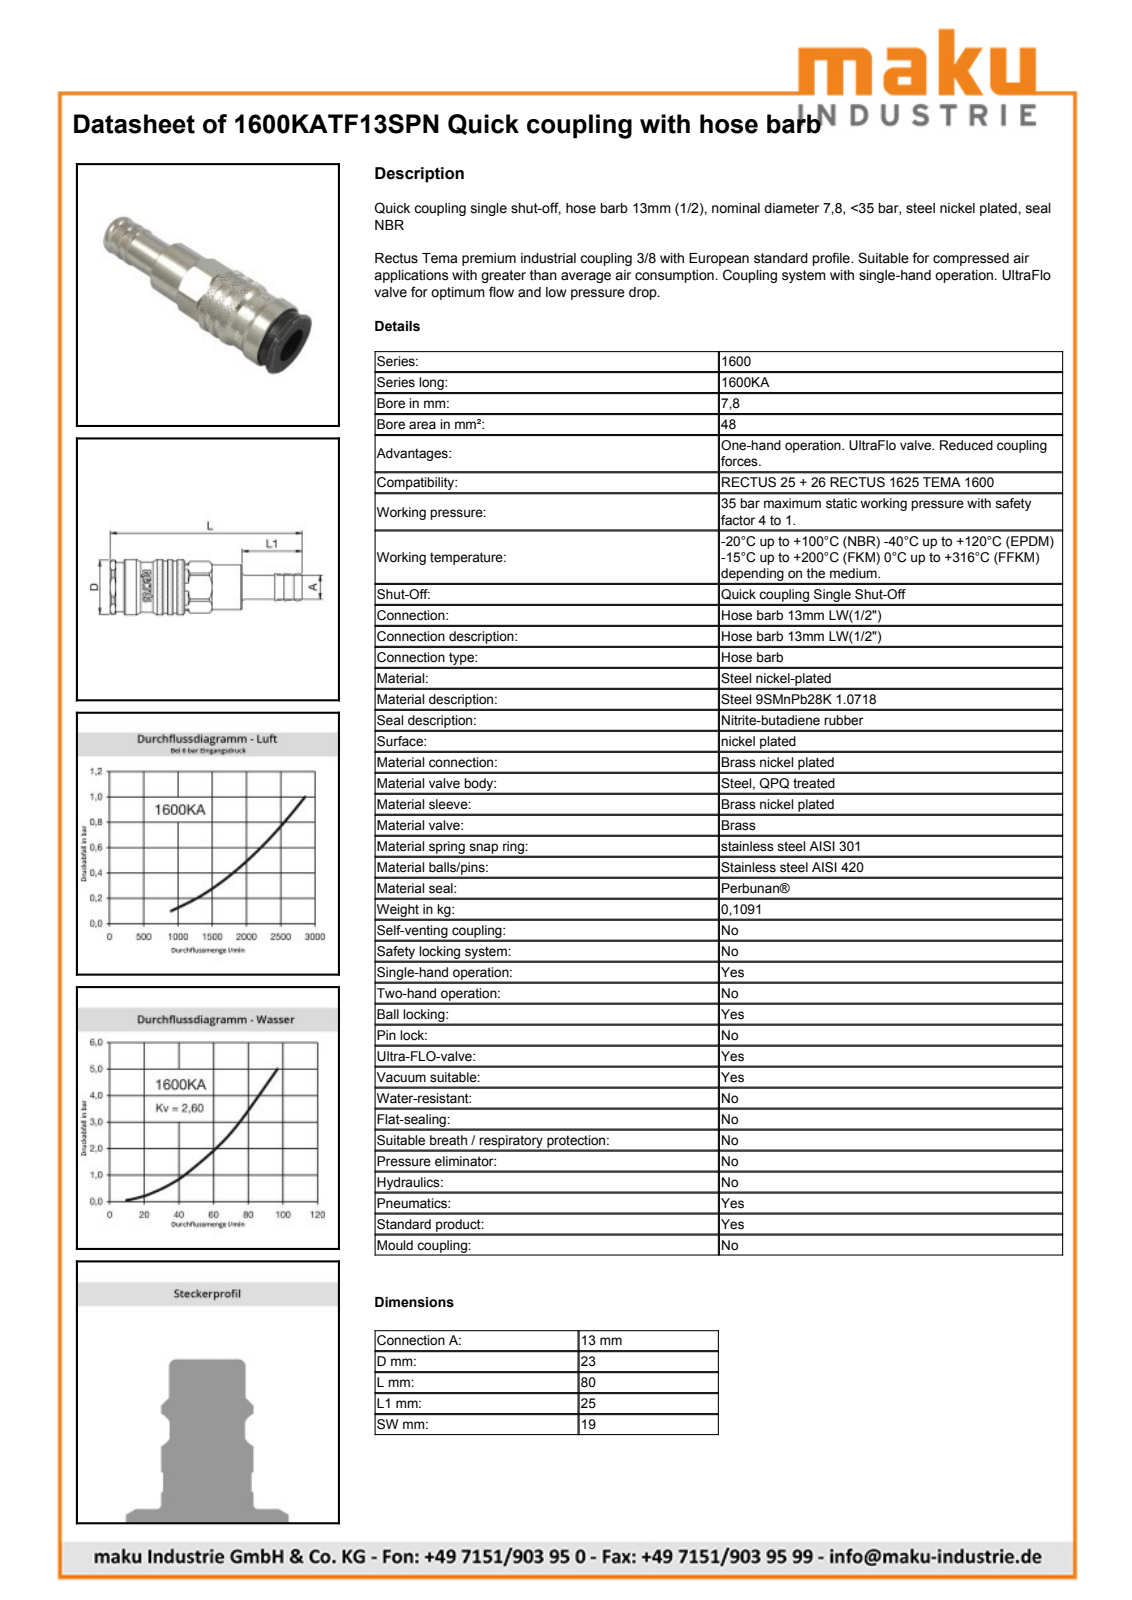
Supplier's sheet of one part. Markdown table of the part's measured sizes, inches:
| quantity | value |
| --- | --- |
| part name | D106873 |
| STEP written by | Autodesk Inventor 2013 (AUTOMOTIVE_DESIGN) |
| units | inches |
| bodies | 2 solids, 637 faces (211 planar, 92 cylindrical, 334 other) |
| overall size | 3.133 × 0.911 × 0.911 |
| volume | 1.283 in³ |
| surface area | 14.91 in² |
| round holes (diameter × count) | 0.636 × 1, 0.677 × 1, 0.705 × 1, 0.772 × 1, 0.815 × 1 |
| round bosses / shafts (diameter × count) | 0.911 × 1, 0.866 × 1, 0.827 × 1, 0.799 × 1, 0.74 × 1, 0.693 × 1, 0.669 × 1, 0.618 × 1 |
| partial cylindrical surfaces (radius × count) | 0.306 × 1, 0.38 × 1, 0.409 × 1, 0.421 × 1, 0.443 × 1 |
| main face-to-face distances | 0.748, 3.133, 2.149, 0.984, 1.222, 0.927, 1.911, 2.087, 1.047, 0.175 |
